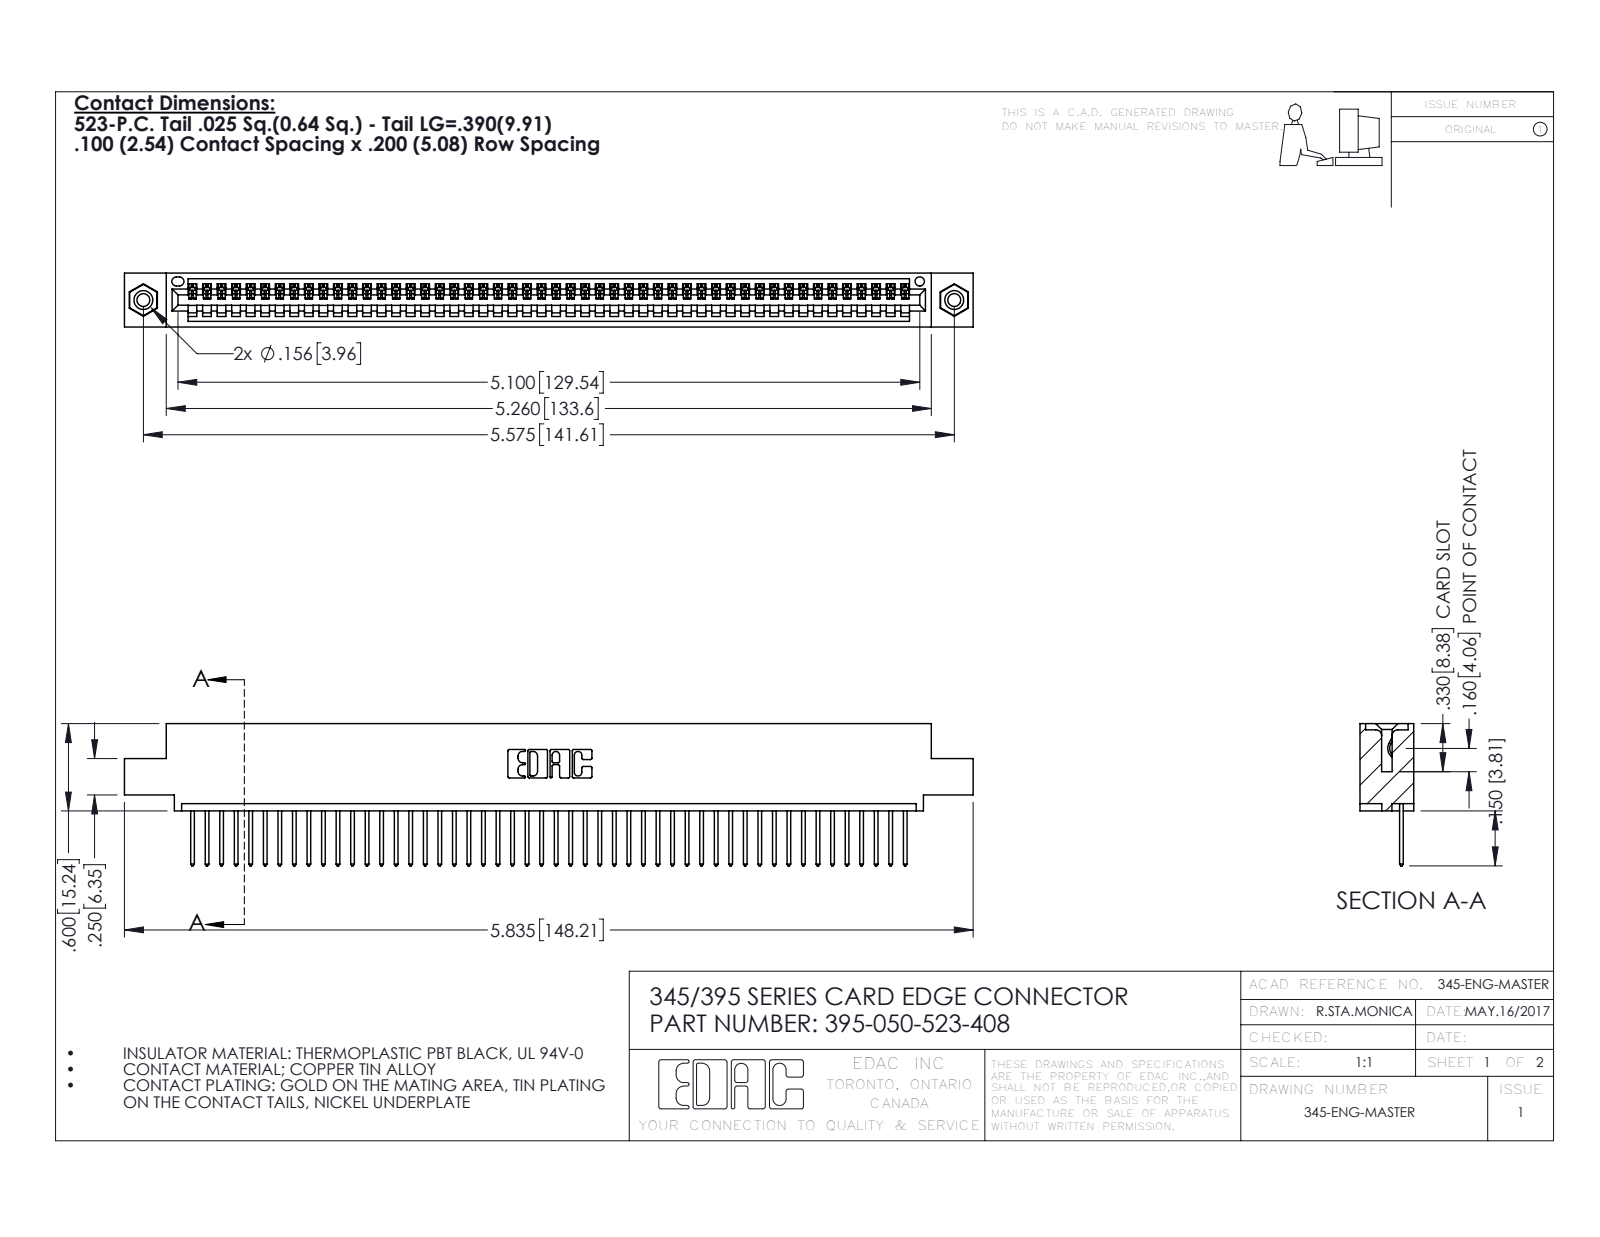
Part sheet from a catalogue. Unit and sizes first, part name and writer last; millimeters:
Units: millimetres
Overall size (bounding box): 148.2 × 24.8 × 9.4
Round holes (diameter × count): ⌀2.3 ×2, ⌀3.2 ×2, ⌀4 ×2, ⌀1.6 ×1
Round bosses / shafts (diameter × count): ⌀3.9 ×2
Partial cylindrical surfaces — rounded edges, fillets, slot ends (radius × count): R0.2 ×100, R0.3 ×100, R0.3 ×22, R0.2 ×6, R0.8 ×6, R0.7 ×3, R0.8 ×2, R1 ×2
Main face-to-face distances: 1.8, 7.6, 9.4, 5.1, 2.5, 6.9, 0.6, 5.7, 3.8, 1.8
Hole centre spacings: 6.9, 135.6, 141.6
Volume: 14 000 mm³ · Surface area: 18 930 mm²
Bodies: 53 solids, 3090 faces (2116 planar, 958 cylindrical, 16 other)
Part name (STEP PRODUCT): 345-250-001_345-250-003-102; 395-050-523-408; 345-292-001_345-293-123; 345 Part_0.110 Offset - 0.156 Dia-TI
STEP written by: SolidWorks 2016 (CONFIG_CONTROL_DESIGN)
